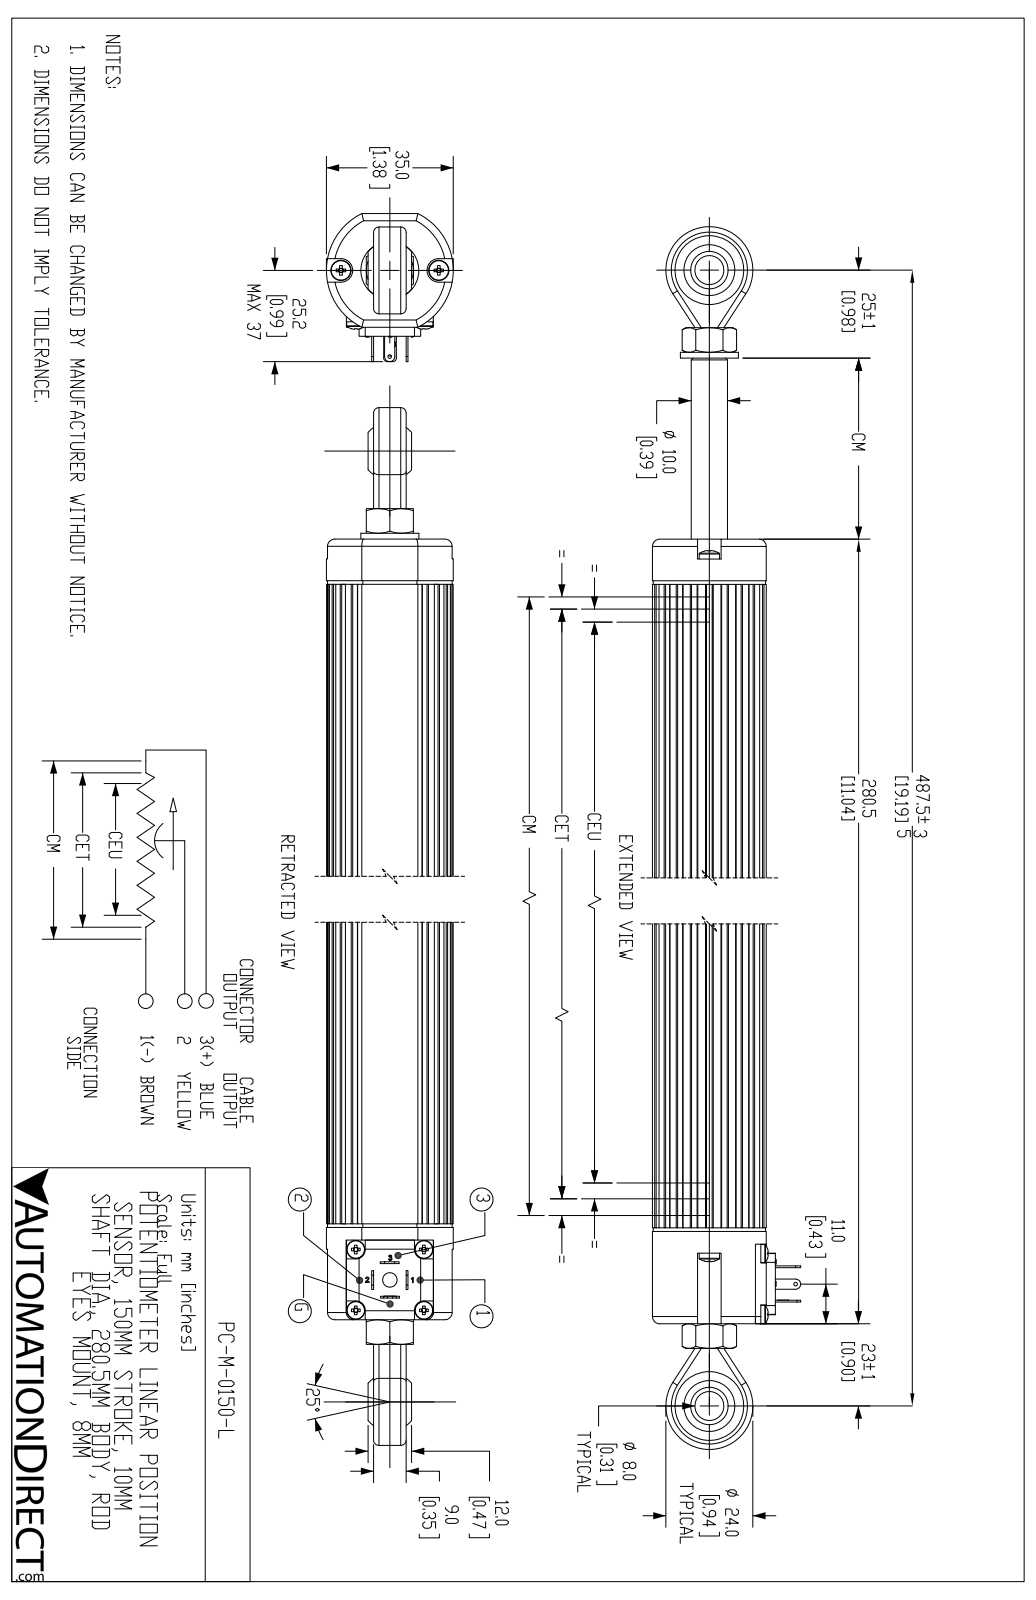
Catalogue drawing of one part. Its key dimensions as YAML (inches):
part_name: "PC-M-0150-L"
step_written_by: "SolidWorks 2019 (AUTOMOTIVE_DESIGN)"
units: inches
bodies: {solids: 26, faces: 1441, planar: 437, cylindrical: 366, other: 638}
overall_size: [14.08, 1.61, 1.378]
volume: 17.4
surface_area: 102.2
round_holes:
  - {diameter: 0.087, count: 4}
  - {diameter: 0.102, count: 4}
  - {diameter: 0.039, count: 3}
  - {diameter: 0.108, count: 2}
  - {diameter: 0.138, count: 2}
  - {diameter: 0.315, count: 2}
  - {diameter: 0.748, count: 2}
  - {diameter: 0.114, count: 1}
  - {diameter: 0.157, count: 1}
  - {diameter: 0.268, count: 1}
  - {diameter: 0.331, count: 1}
  - {diameter: 0.512, count: 1}
round_bosses_or_shafts:
  - {diameter: 0.197, count: 4}
  - {diameter: 0.098, count: 4}
  - {diameter: 0.118, count: 3}
  - {diameter: 0.22, count: 2}
  - {diameter: 0.63, count: 1}
  - {diameter: 0.394, count: 1}
  - {diameter: 0.39, count: 1}
  - {diameter: 0.315, count: 1}
partial_cylinders:
  - {radius: 0.059, count: 8}
  - {radius: 0.039, count: 5}
  - {radius: 0.079, count: 5}
  - {radius: 0.102, count: 4}
  - {radius: 0.118, count: 4}
  - {radius: 0.055, count: 2}
  - {radius: 0.128, count: 2}
  - {radius: 0.472, count: 2}
face_to_face_distances: [1.236, 0.039, 9.547, 9.508, 9.587, 0.118, 1.118, 0.913, 0.913, 10.591]
hole_center_spacings: [0.496, 0.531, 0.661, 0.74, 0.993, 0.024, 0.11, 0.134]
